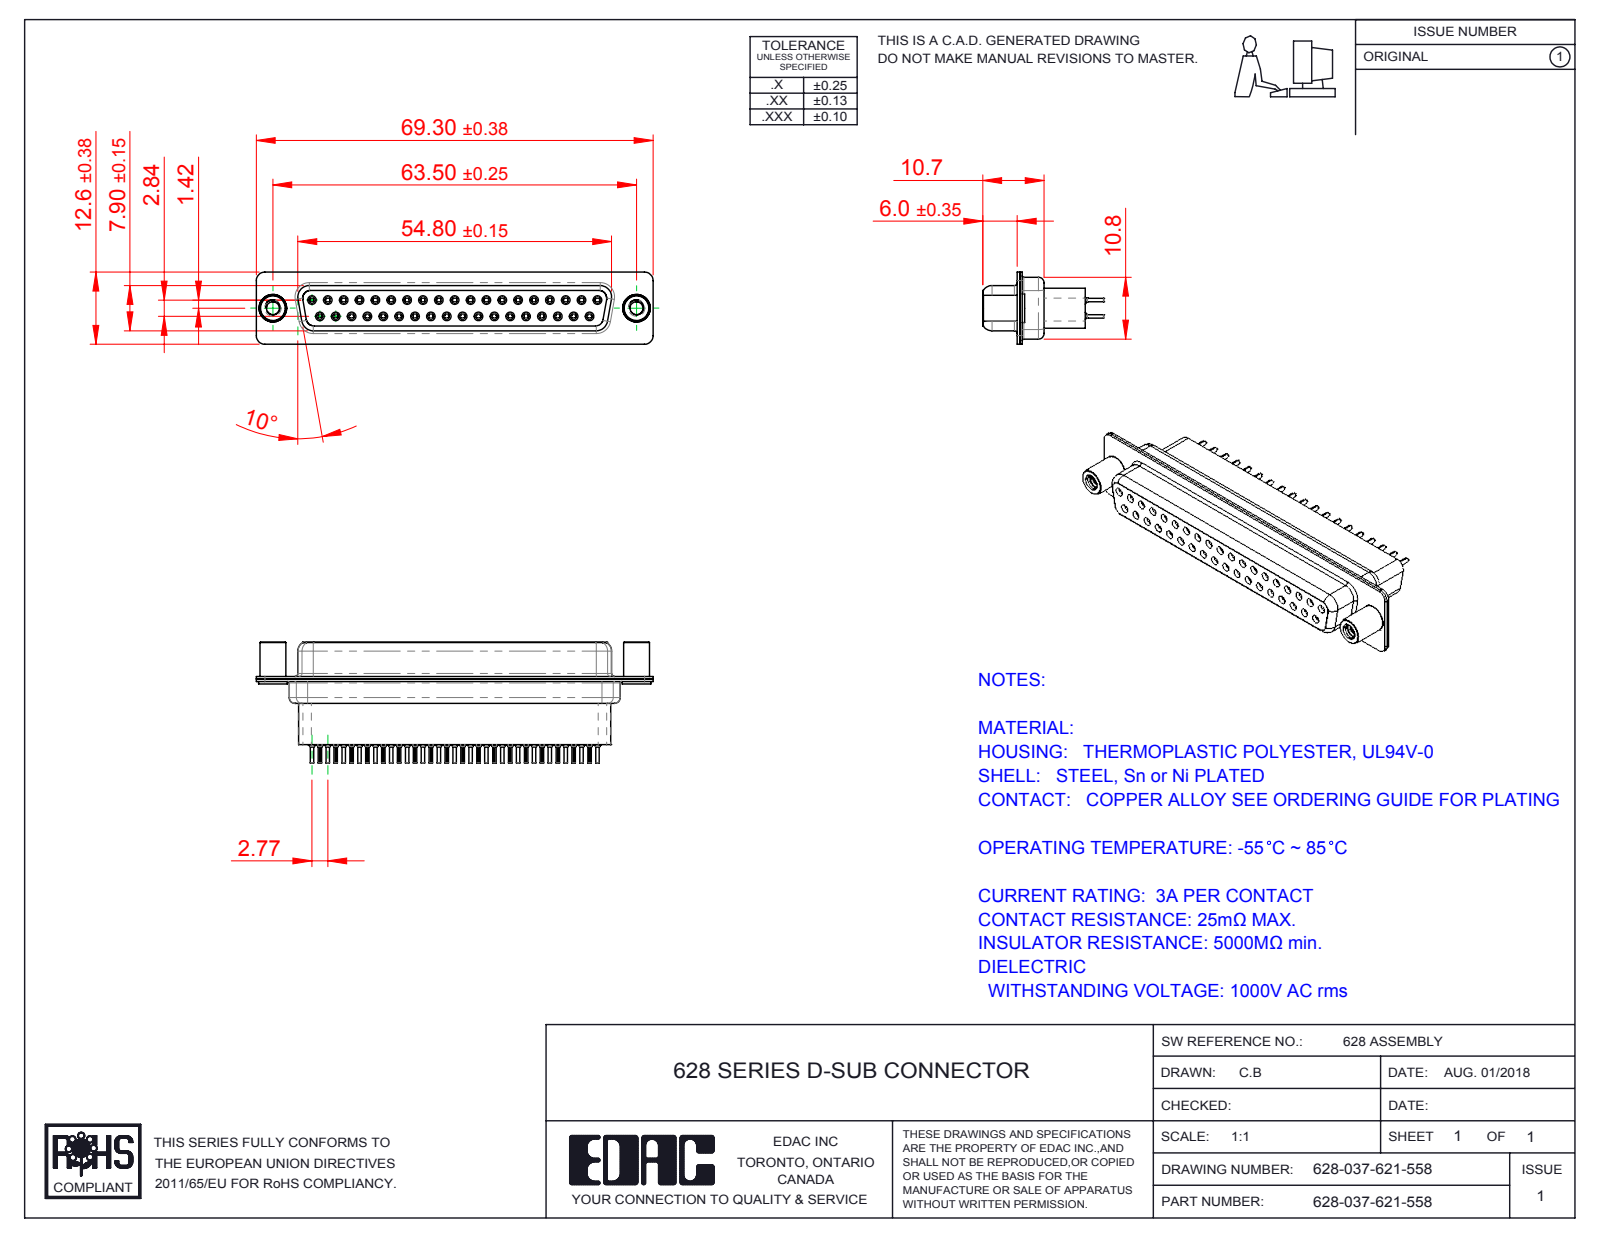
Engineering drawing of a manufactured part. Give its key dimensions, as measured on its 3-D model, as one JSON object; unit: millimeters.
{"part_name": "628 Housing_37 HP; 628 4-40 Threaded Standoff; 628-037-621-558; 628 Shell Rear_37 Contacts (+3 more)", "step_written_by": "SolidWorks 2016 (CONFIG_CONTROL_DESIGN)", "units": "millimeters", "bodies": {"solids": 42, "faces": 4837, "planar": 1213, "cylindrical": 1373, "other": 2251}, "overall_size": [69.3, 21.1, 12.6], "volume_mm3": 7610, "surface_area_mm2": 17001, "round_holes": [[0.2, 37], [0.8, 37], [0.9, 37], [1.1, 37], [1.6, 37], [1.7, 19], [2.26, 2], [4, 2], [4.8, 2]], "round_bosses_or_shafts": [[2, 37], [1.5, 37], [1.2, 37], [0.6, 37], [5, 2], [4.9, 2], [4.5, 2]], "partial_cylinders_radius": [[0.1, 74], [0.28, 37], [1.5, 16], [2, 12], [0.25, 4], [0.5, 4], [0.6, 4], [0.65, 4]], "face_to_face_distances": [0.45, 0.4, 6.6, 6.2, 1.9, 8.5, 0.85, 1.4, 7.05, 7.45], "hole_center_spacings": [3.16, 2.77, 5.54, 8.31, 5.04, 7.49, 11.08, 13.85]}
